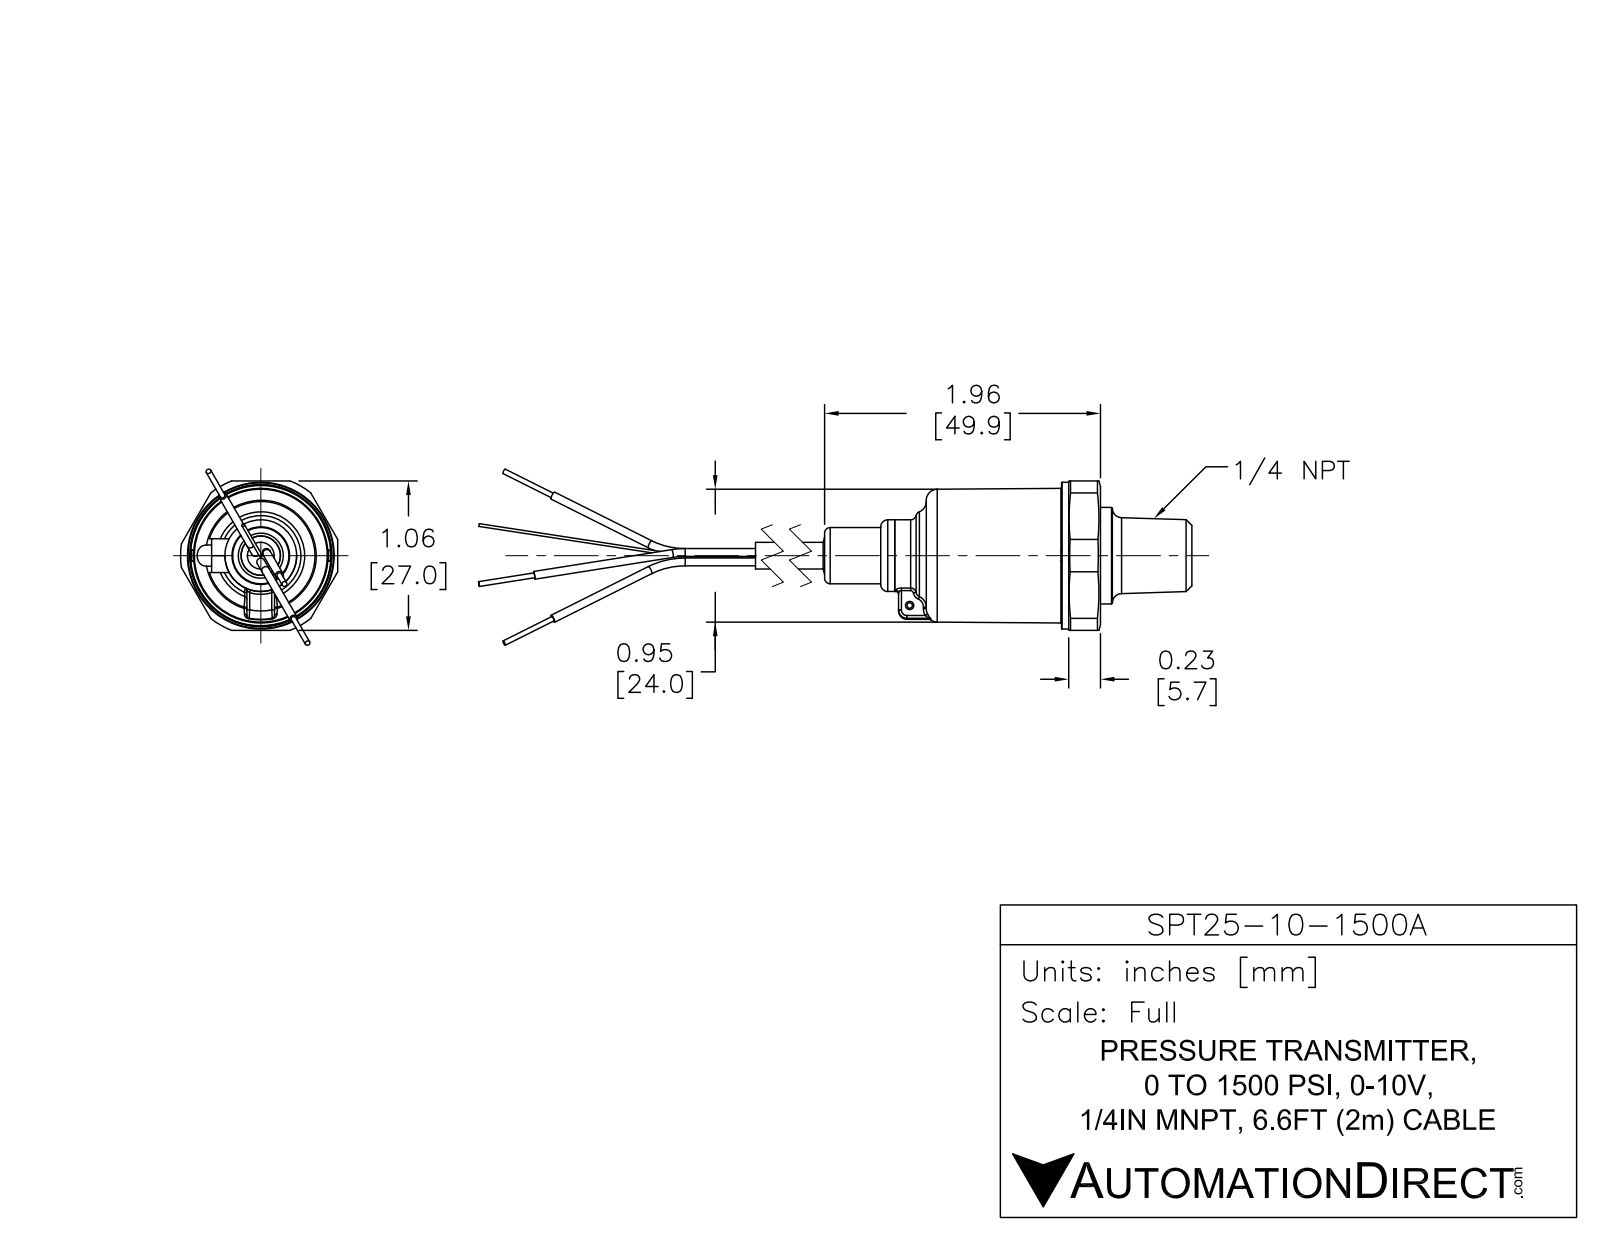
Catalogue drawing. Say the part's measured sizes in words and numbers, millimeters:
The part is named "SPT25-10-1500A". Its 3-D file was written by "SolidWorks 2017 (AUTOMOTIVE_DESIGN)". It is 7 solids with 116 faces: 32 planar, 49 cylindrical and 35 other. Overall it measures 153.3 by 29 by 27.09 millimeters. Its volume is 20 801 cubic millimeters and its surface area 7 170 square millimeters. Round holes: 1 of diameter 1, 1 of diameter 3.3. Round bosses or shafts: 6 of diameter 1.4, 5 of diameter 0.75, 1 of diameter 26.75, 1 of diameter 24, 1 of diameter 17.5, 1 of diameter 14, 1 of diameter 13, 1 of diameter 10. Partial cylindrical surfaces (rounded edges, fillets, slot ends): 1 of radius 2, 1 of radius 14.5. The main face-to-face distances are 6.75, 24, 17.25, 42.75, 49.5, 66.75, 44, 1.25, 5.5, 22.75.
